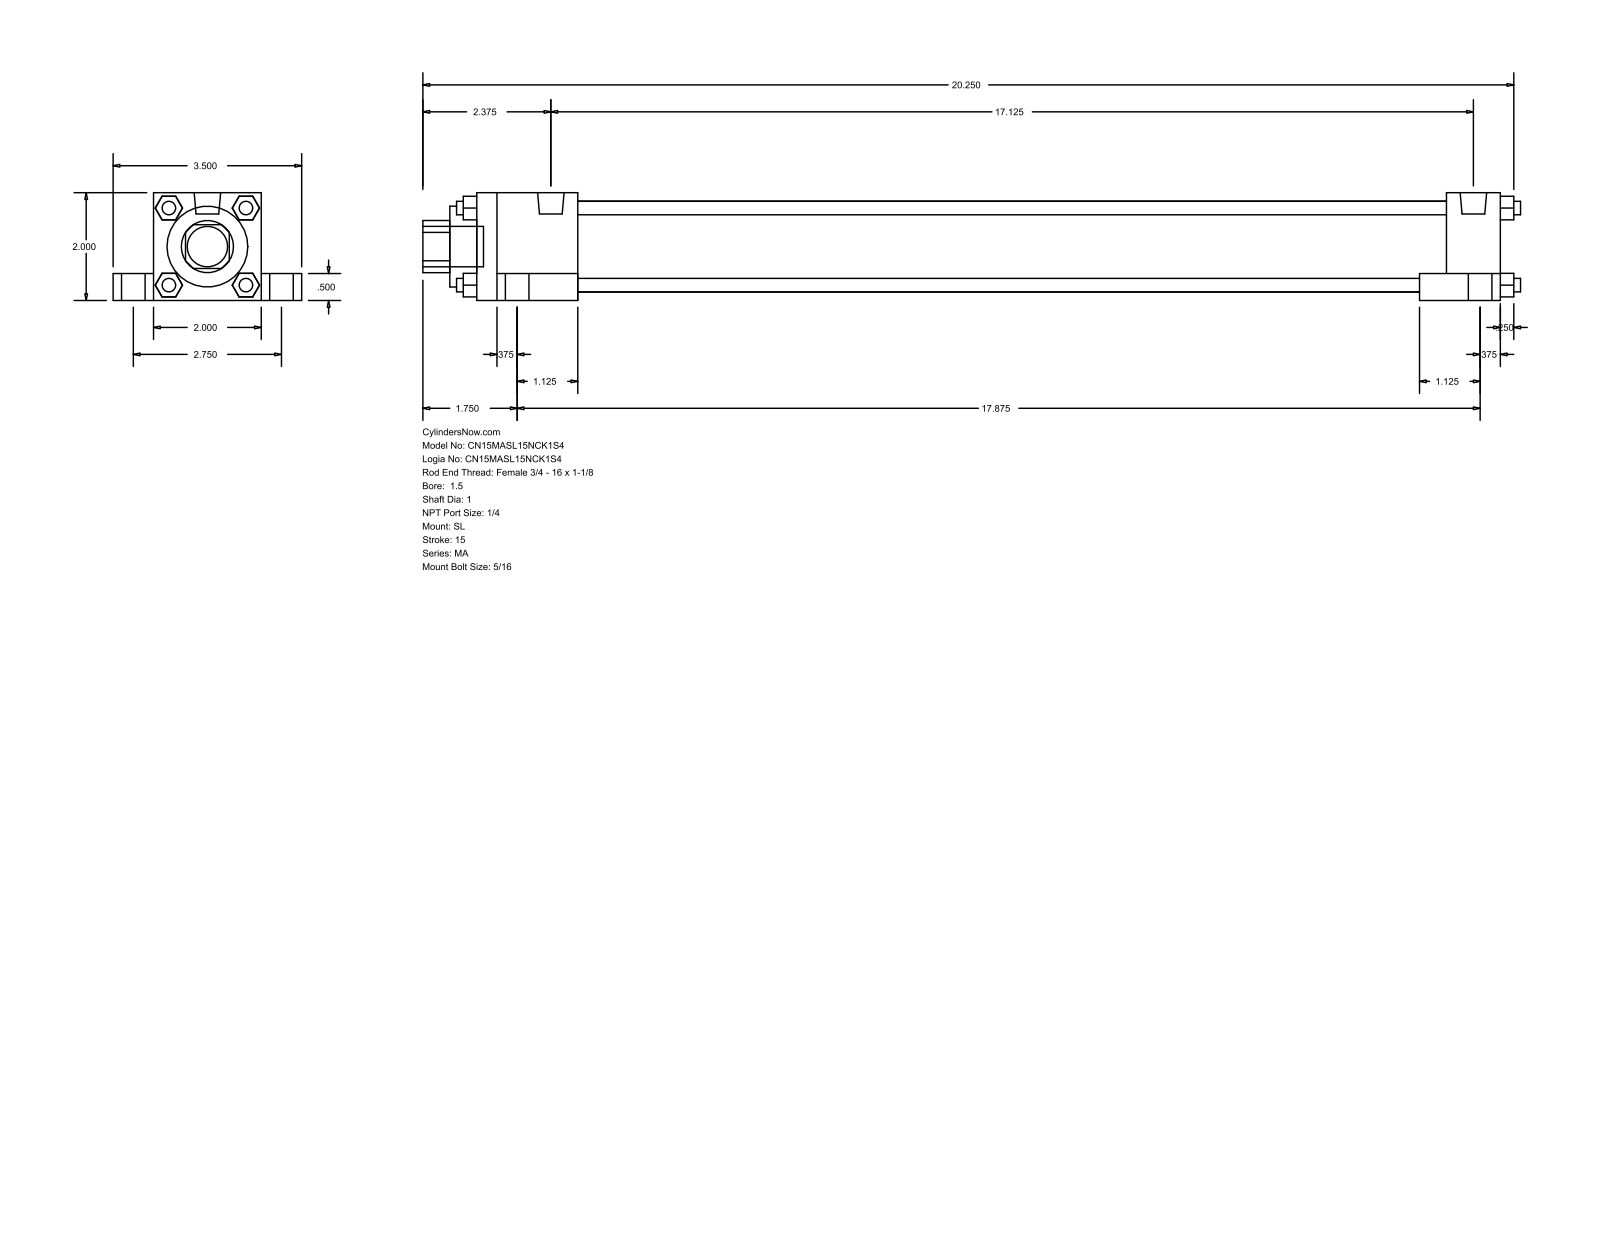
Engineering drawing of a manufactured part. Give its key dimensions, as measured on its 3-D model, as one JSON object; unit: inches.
{"part_name": "MA_SL__0150_1", "step_written_by": "GSSL Pune (CONFIG_CONTROL_DESIGN)", "units": "inches", "bodies": {"solids": 0, "faces": 148, "planar": 112, "cylindrical": 36, "other": 0}, "overall_size": [20.375, 3.5, 2], "round_holes": [[1, 1], [1.5, 1], [1.69, 1]], "round_bosses_or_shafts": [[0.687, 4], [0.437, 4], [0.313, 4], [0.25, 4], [0.492, 2], [0.75, 1]], "partial_cylinders_radius": [[0.484, 1]], "face_to_face_distances": [2, 0.5, 0.75, 0.375, 2.75, 1.5, 0.25, 19, 1, 18]}
